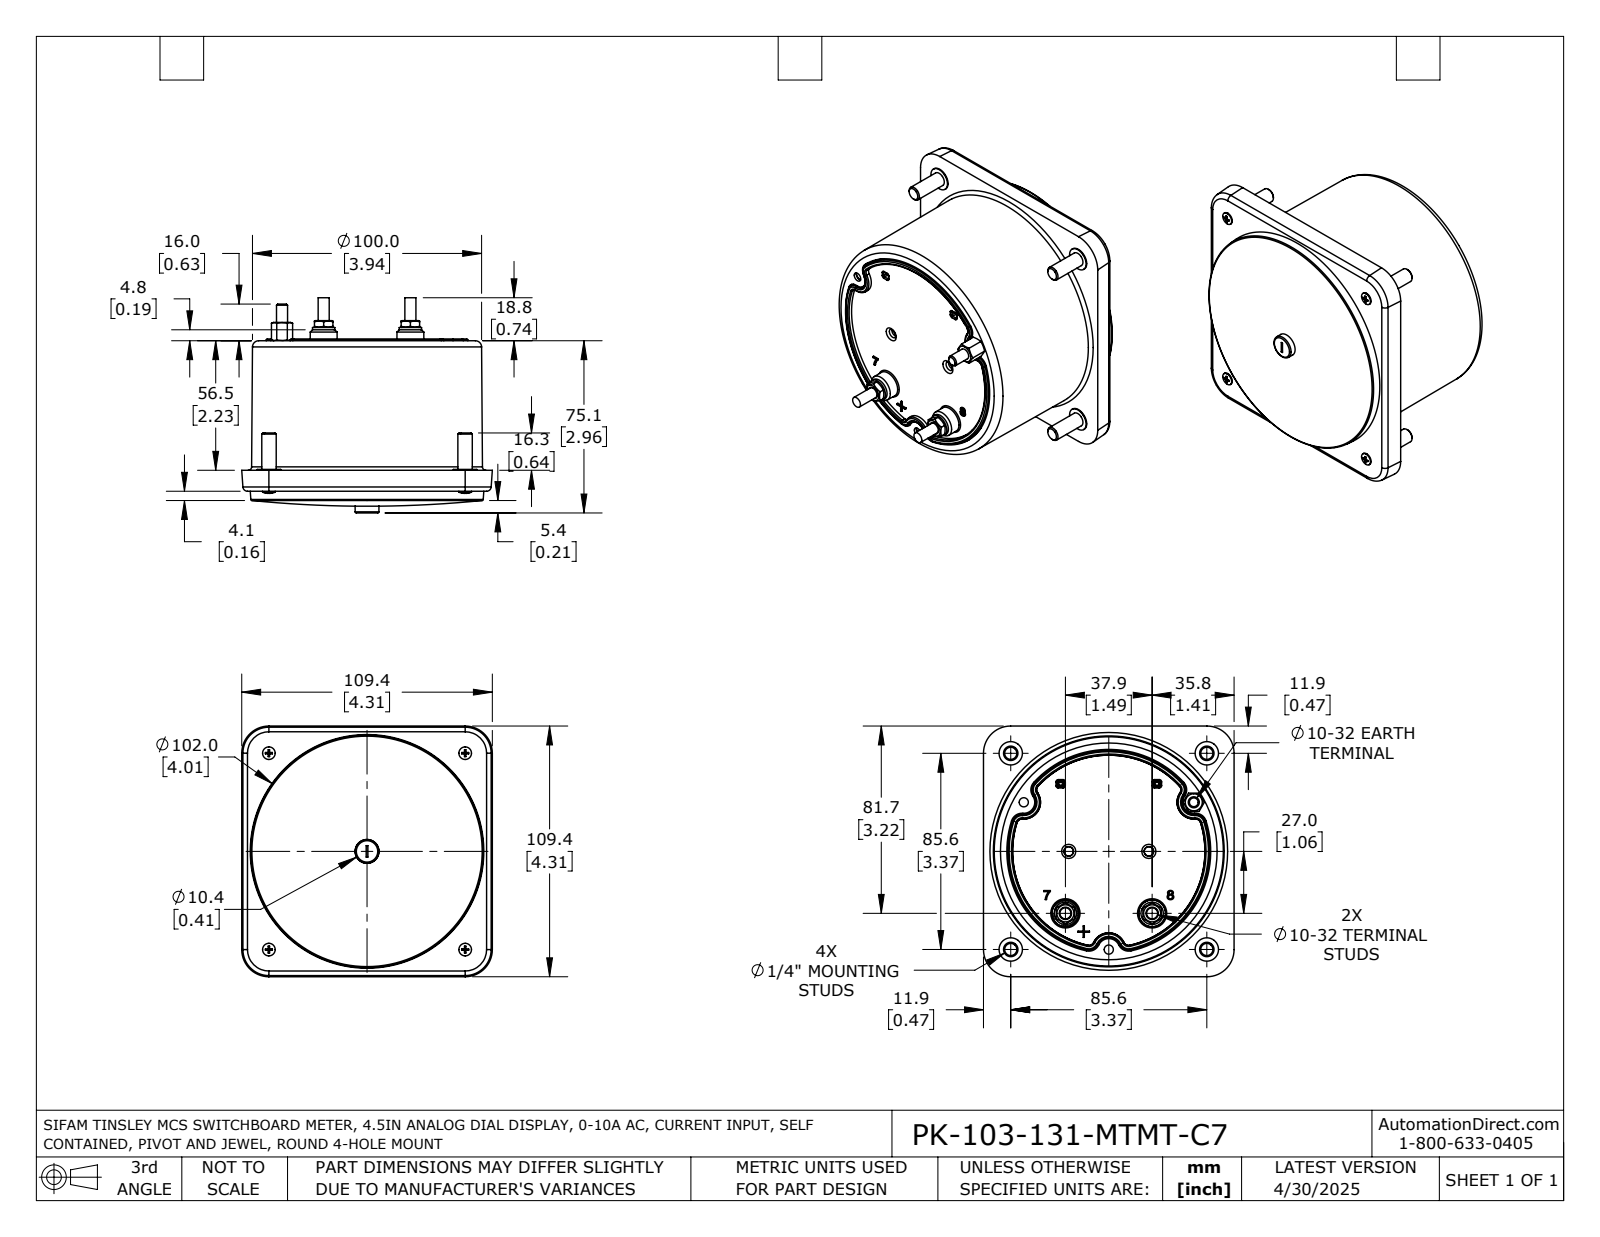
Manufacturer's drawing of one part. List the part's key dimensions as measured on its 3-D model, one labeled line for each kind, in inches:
Part name (STEP PRODUCT): PK-103-131-MTMT-C7
STEP written by: SolidWorks 2021 (AUTOMOTIVE_DESIGN)
Units: inches
Bodies: 1 solid, 609 faces (167 planar, 141 cylindrical, 301 other)
Overall size (bounding box): 4.307 × 4.307 × 3.697
Volume: 36.28 in³ · Surface area: 82.21 in²
Round holes (diameter × count): ⌀0.094 ×4, ⌀0.138 ×4, ⌀0.315 ×4, ⌀0.157 ×3, ⌀0.209 ×2
Round bosses / shafts (diameter × count): ⌀0.402 ×4, ⌀0.248 ×4, ⌀0.217 ×4, ⌀0.114 ×4, ⌀0.19 ×3, ⌀0.384 ×2, ⌀0.146 ×1
Partial cylindrical surfaces — rounded edges, fillets, slot ends (radius × count): R0.02 ×24, R0.189 ×9, R0.079 ×4, R1.752 ×1
Main face-to-face distances: 2.177, 2.537, 0.36, 0.048, 2.225, 2.585, 0.489, 2.715, 2.667, 0.129
Hole centre spacings: 3.372, 3.37, 3.374, 3.378, 3.38, 4.769, 0.971, 1.126
